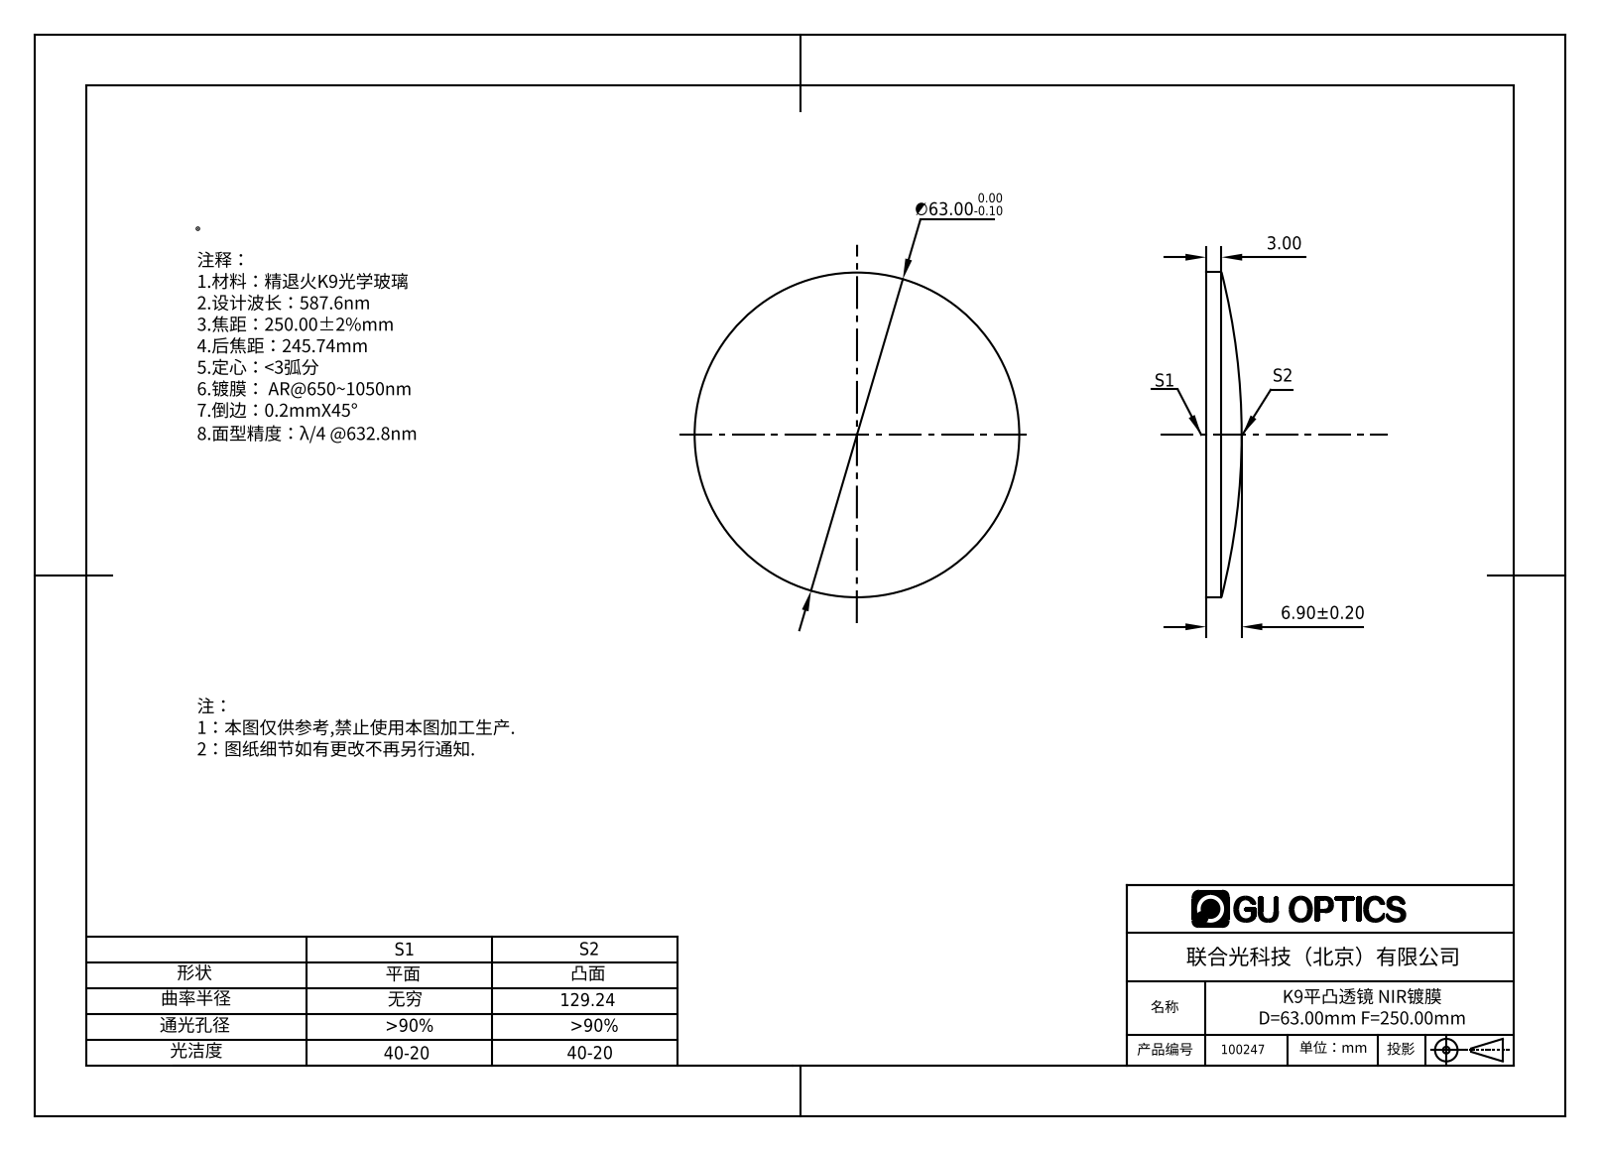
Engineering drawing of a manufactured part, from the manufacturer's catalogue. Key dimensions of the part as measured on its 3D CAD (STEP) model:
Part name (STEP PRODUCT): 100247
STEP written by: SolidWorks 2016 (AUTOMOTIVE_DESIGN)
Units: millimetres
Bodies: 1 solid, 5 faces (1 planar, 2 cylindrical, 2 other)
Overall size (bounding box): 63 × 63 × 6.9
Volume: 15 461 mm³ · Surface area: 6 876 mm²
Round bosses / shafts (diameter × count): ⌀63 ×1
